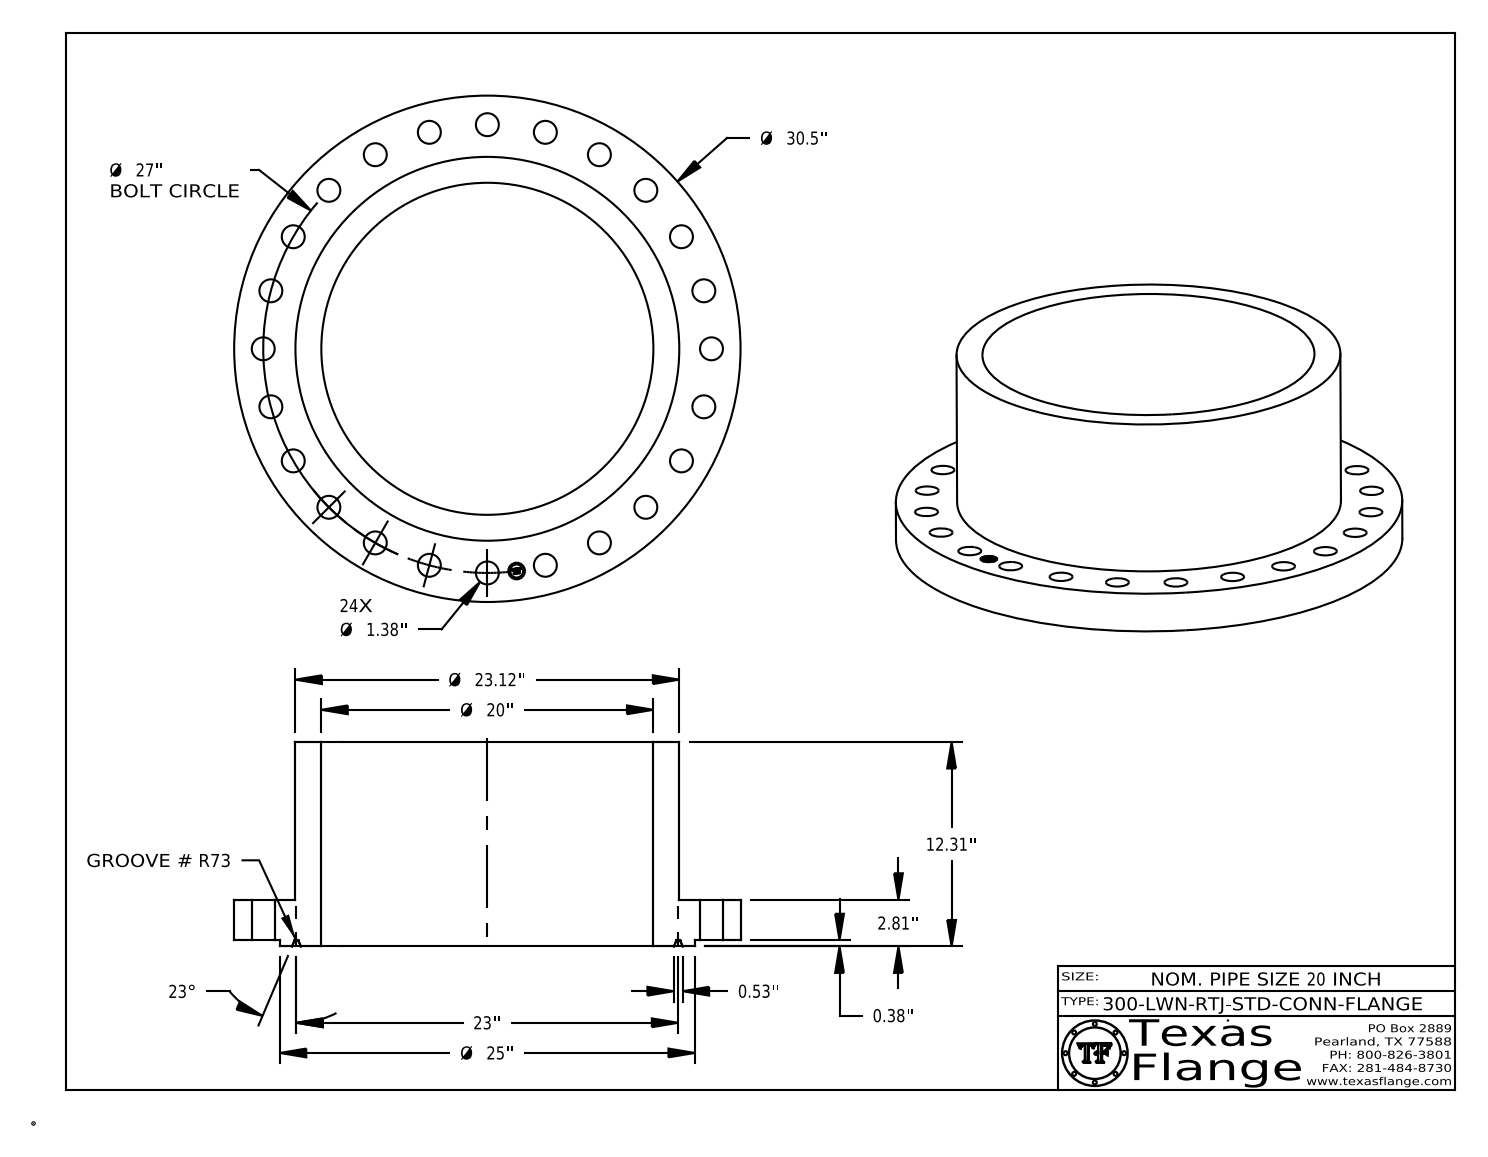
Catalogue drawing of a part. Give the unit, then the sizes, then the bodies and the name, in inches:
Units: inches
Overall size (bounding box): 30.5 × 30.5 × 12.313
Round holes (diameter × count): ⌀1.38 ×24, ⌀1 ×1, ⌀20 ×1
Round bosses / shafts (diameter × count): ⌀0.061 ×8, ⌀30.5 ×1, ⌀25 ×1, ⌀23.12 ×1, ⌀0.788 ×1
Main face-to-face distances: 2.437, 0.375, 2.813, 12.313, 11.937, 9.5, 2.808, 2.433, 9.505, 0.298
Hole centre spacings: 13.5, 3.524, 6.988, 10.333, 16.437, 24.945, 26.769, 21.421
Volume: 1 988 in³ · Surface area: 2 776 in²
Bodies: 1 solid, 455 faces (371 planar, 76 cylindrical, 8 other)
Part name (STEP PRODUCT): 20-300-LWN-RTJ-STD-CONN-FLANGE
STEP written by: CATIA V5 STEP AP214 (AUTOMOTIVE_DESIGN)
